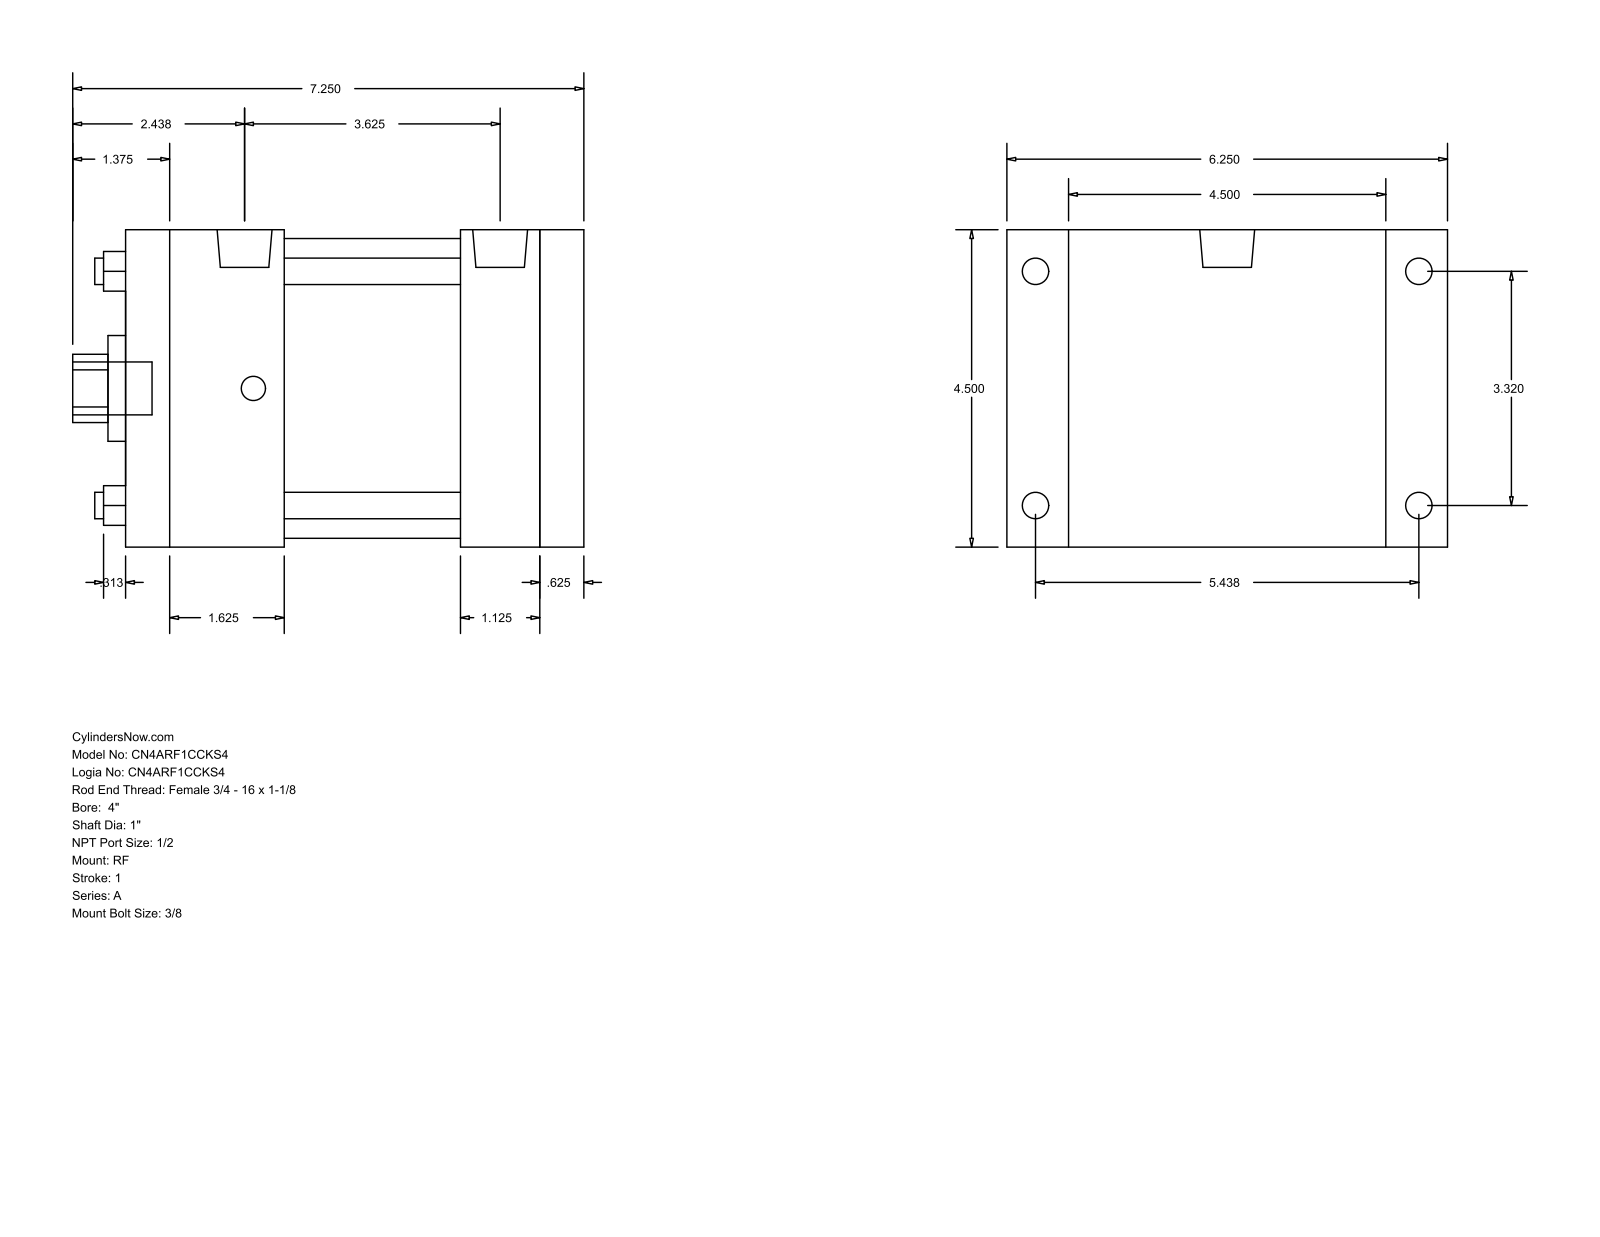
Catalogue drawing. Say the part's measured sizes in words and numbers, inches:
The part is named "A_RF__0400_1". Its 3-D file was written by "GSSL Pune (CONFIG_CONTROL_DESIGN)". It is 0 solids with 92 faces: 64 planar, 28 cylindrical and 0 other. Overall it measures 7.25 by 6.25 by 4.5 inches. Round holes: 4 of diameter 0.375, 1 of diameter 1, 1 of diameter 1.5, 1 of diameter 4.25. Round bosses or shafts: 4 of diameter 0.375, 4 of diameter 0.344, 2 of diameter 0.778, 1 of diameter 0.75. Partial cylindrical surfaces (rounded edges, fillets, slot ends): 1 of radius 0.484. The main face-to-face distances are 4.5, 6.5, 0.625, 5.875, 2.5, 0.875, 5.375, 4.75, 1.125, 1.75. The hole center spacings are 2.347, 3.32, 4.695.
